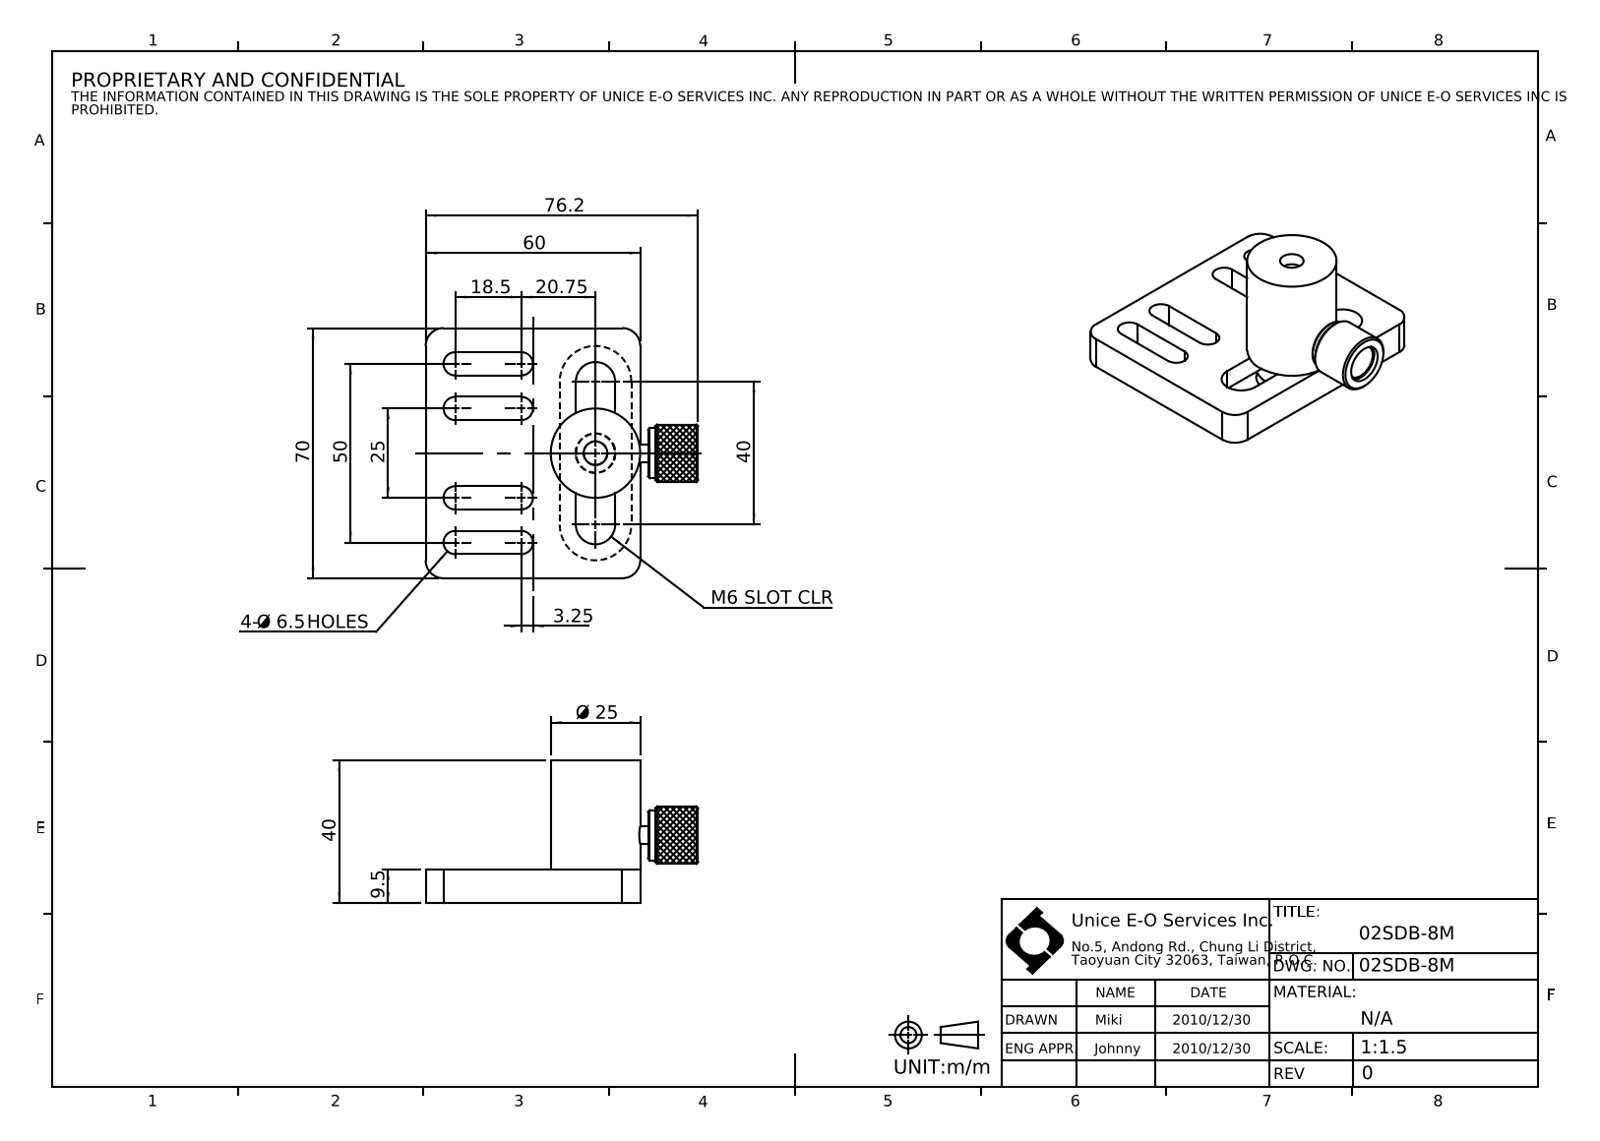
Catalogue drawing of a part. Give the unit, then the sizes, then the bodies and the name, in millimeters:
Units: millimetres
Overall size (bounding box): 76.2 × 70 × 40
Round holes (diameter × count): ⌀6.6 ×1, ⌀10.5 ×1, ⌀11 ×1
Round bosses / shafts (diameter × count): ⌀25 ×1, ⌀20 ×1, ⌀16 ×1, ⌀14 ×1
Partial cylindrical surfaces — rounded edges, fillets, slot ends (radius × count): R3.25 ×8, R5 ×4, R5.5 ×2, R10 ×2
Main face-to-face distances: 9.5, 6, 37.5, 3.5, 12.5, 6.5, 60, 70, 30.5, 36.5
Bodies: 0 solids, 83 faces (43 planar, 34 cylindrical, 6 other)
Part name (STEP PRODUCT): 02SDB-8M
STEP written by: SolidWorks 2016 (CONFIG_CONTROL_DESIGN)
